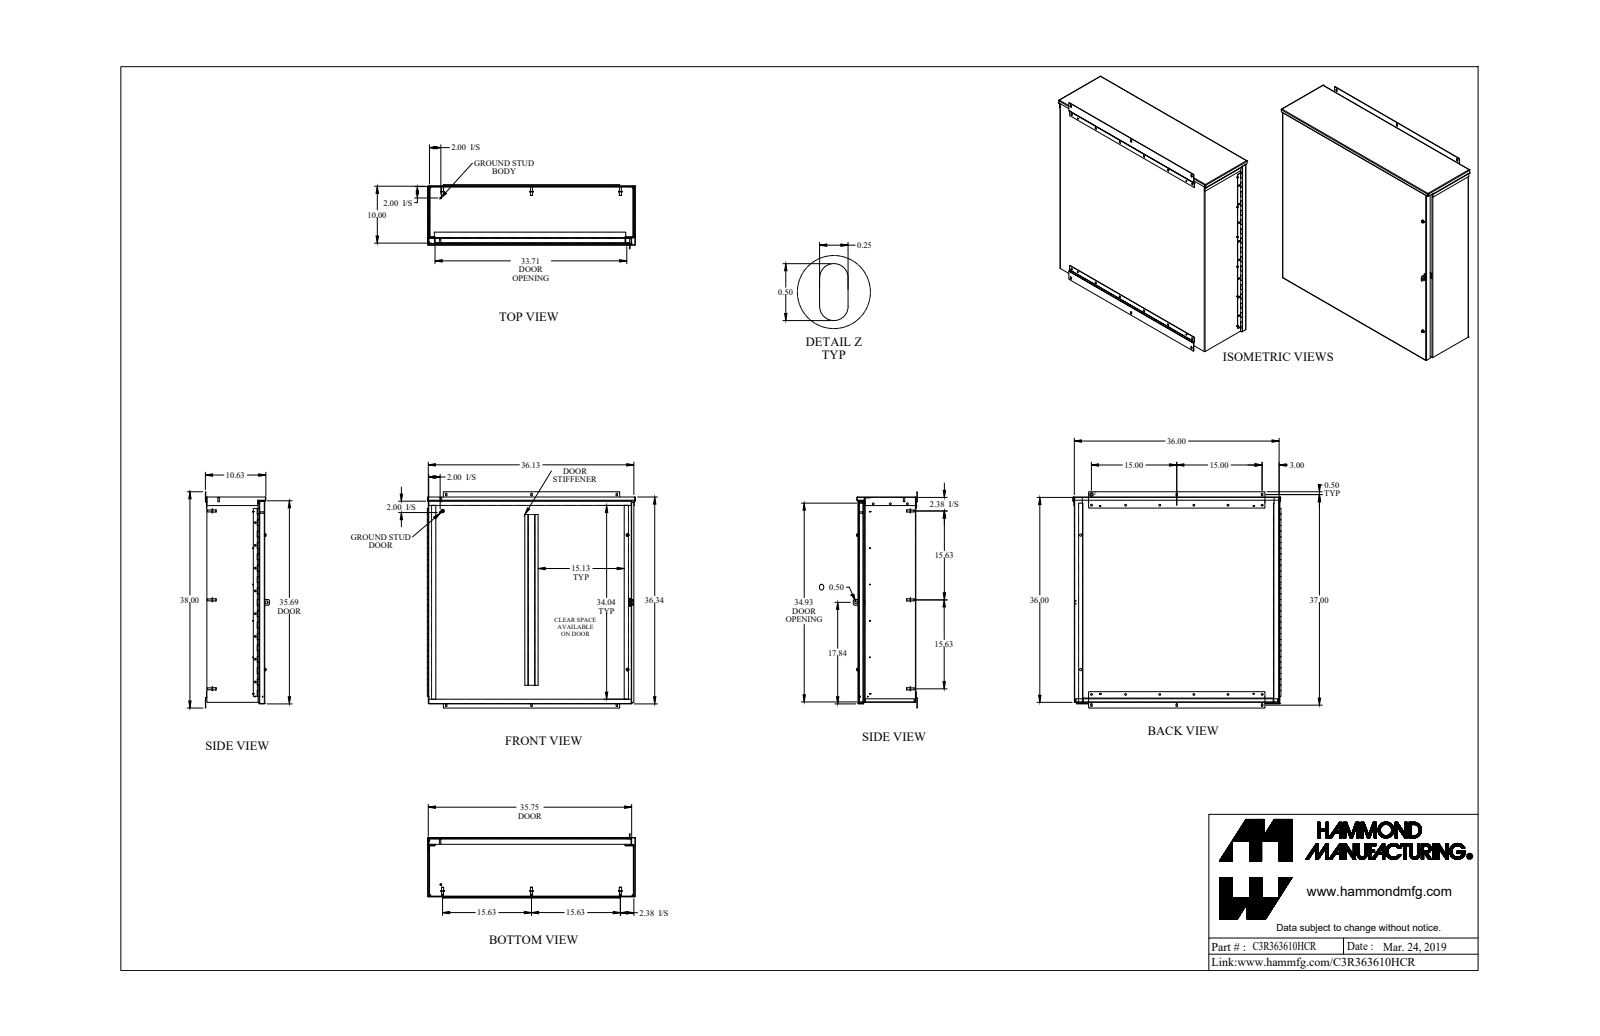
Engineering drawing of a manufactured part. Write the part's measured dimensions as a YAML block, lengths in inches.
part_name: "C3R363610HCR_Default"
step_written_by: "SolidWorks 2019 (CONFIG_CONTROL_DESIGN)"
units: inches
bodies: {solids: 39, faces: 1170, planar: 609, cylindrical: 475, other: 86}
overall_size: [38, 36.571, 11.26]
volume: 374.4
surface_area: 10195
round_holes:
  - {diameter: 0.312, count: 12}
  - {diameter: 0.304, count: 11}
  - {diameter: 0.137, count: 4}
  - {diameter: 0.14, count: 4}
  - {diameter: 0.26, count: 3}
  - {diameter: 0.313, count: 3}
  - {diameter: 0.266, count: 2}
  - {diameter: 0.28, count: 2}
  - {diameter: 0.29, count: 2}
  - {diameter: 0.397, count: 2}
  - {diameter: 0.188, count: 1}
  - {diameter: 0.5, count: 1}
round_bosses_or_shafts:
  - {diameter: 0.131, count: 12}
  - {diameter: 0.65, count: 8}
  - {diameter: 0.375, count: 8}
  - {diameter: 0.33, count: 8}
  - {diameter: 0.51, count: 3}
  - {diameter: 0.244, count: 3}
  - {diameter: 0.187, count: 3}
  - {diameter: 0.5, count: 2}
partial_cylinders:
  - {radius: 0.036, count: 39}
  - {radius: 0.108, count: 39}
  - {radius: 0.125, count: 23}
  - {radius: 0.171, count: 3}
  - {radius: 0.25, count: 2}
face_to_face_distances: [0.072, 10.1, 10.172, 10.028, 36, 35.928, 36.072, 35.856, 0.259, 0.187]
hole_center_spacings: [12, 6, 33.787, 4, 35.35, 8, 18, 24]
